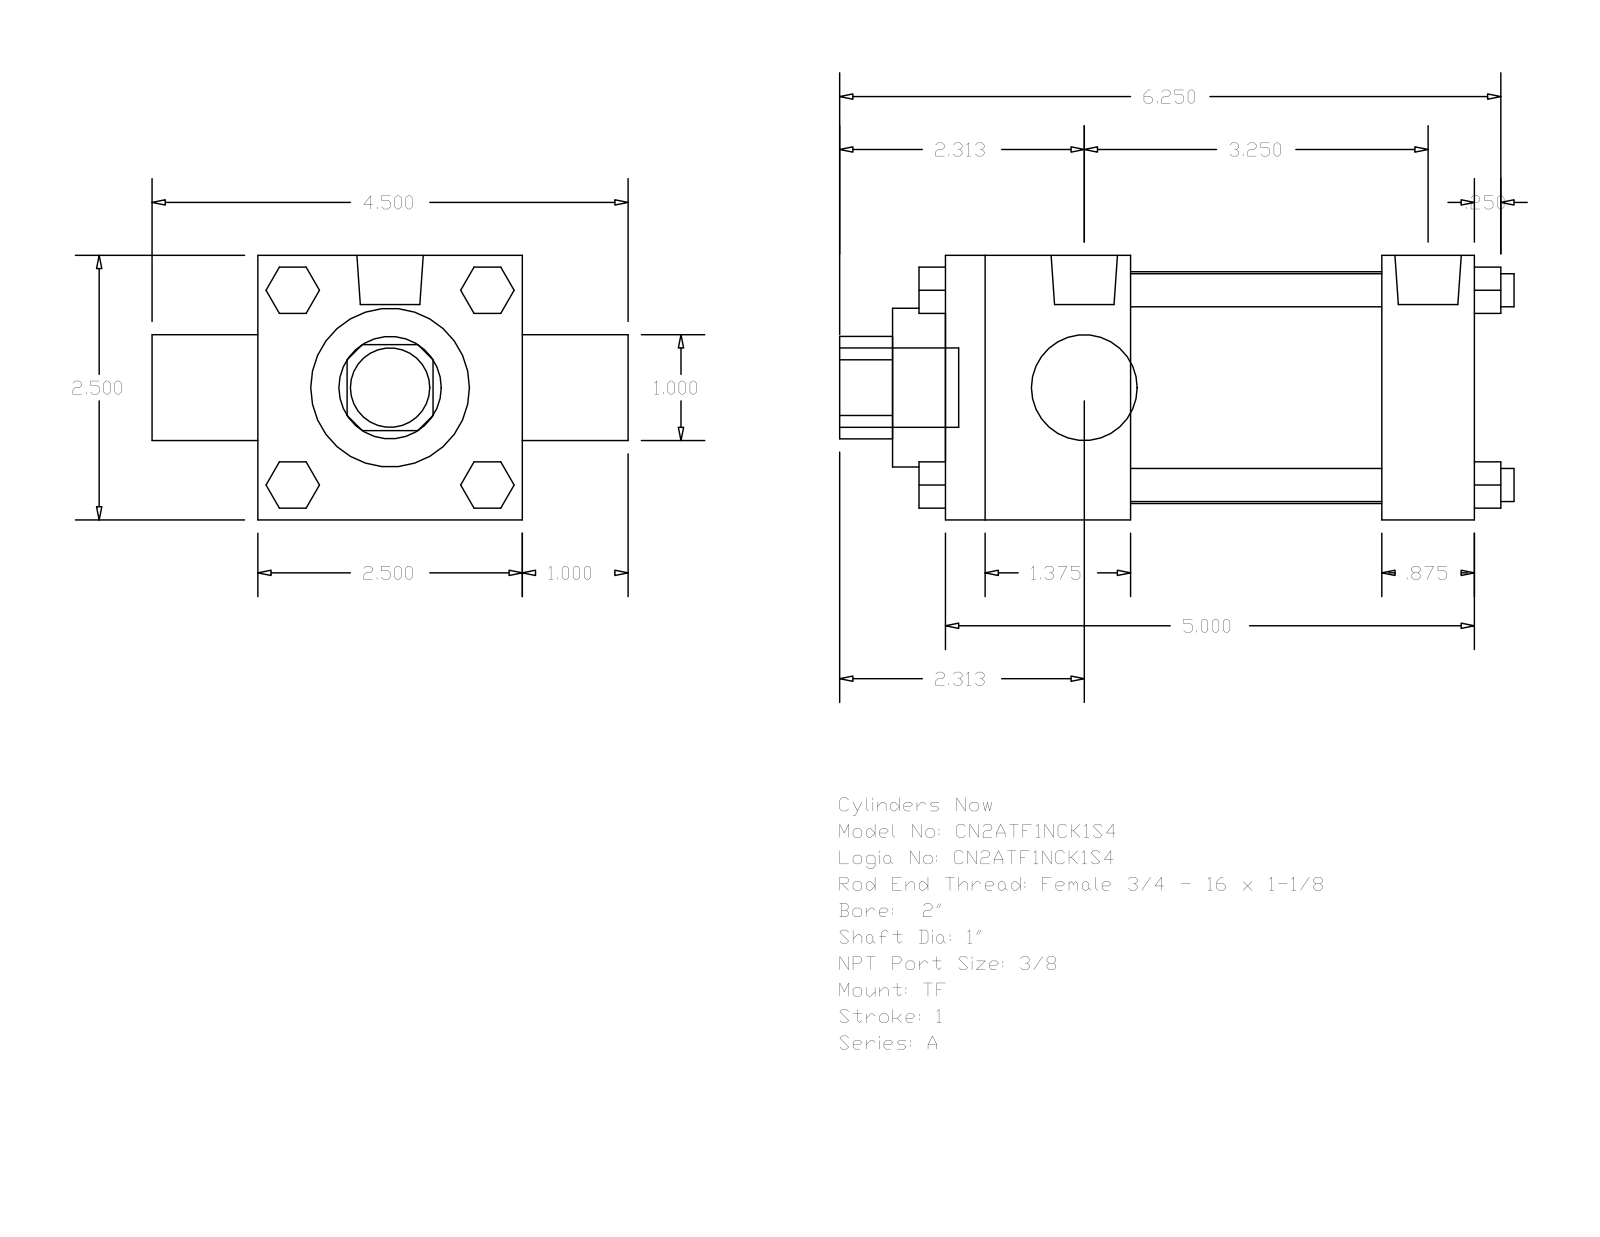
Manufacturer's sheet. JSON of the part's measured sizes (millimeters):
{"part_name": "A_TF__0200_1", "step_written_by": "GSSL Pune (CONFIG_CONTROL_DESIGN)", "units": "millimeters", "bodies": {"solids": 0, "faces": 120, "planar": 92, "cylindrical": 28, "other": 0}, "overall_size": [161.93, 114.3, 63.5], "round_holes": [[25.4, 2], [38.1, 1], [55.63, 1]], "round_bosses_or_shafts": [[7.94, 4], [5.56, 3], [15.93, 2], [19.05, 1]], "partial_cylinders_radius": [[12.29, 1]], "face_to_face_distances": [63.5, 127, 44.45, 104.78, 60.33, 82.55, 22.22, 88.9, 25.4, 139.7]}
